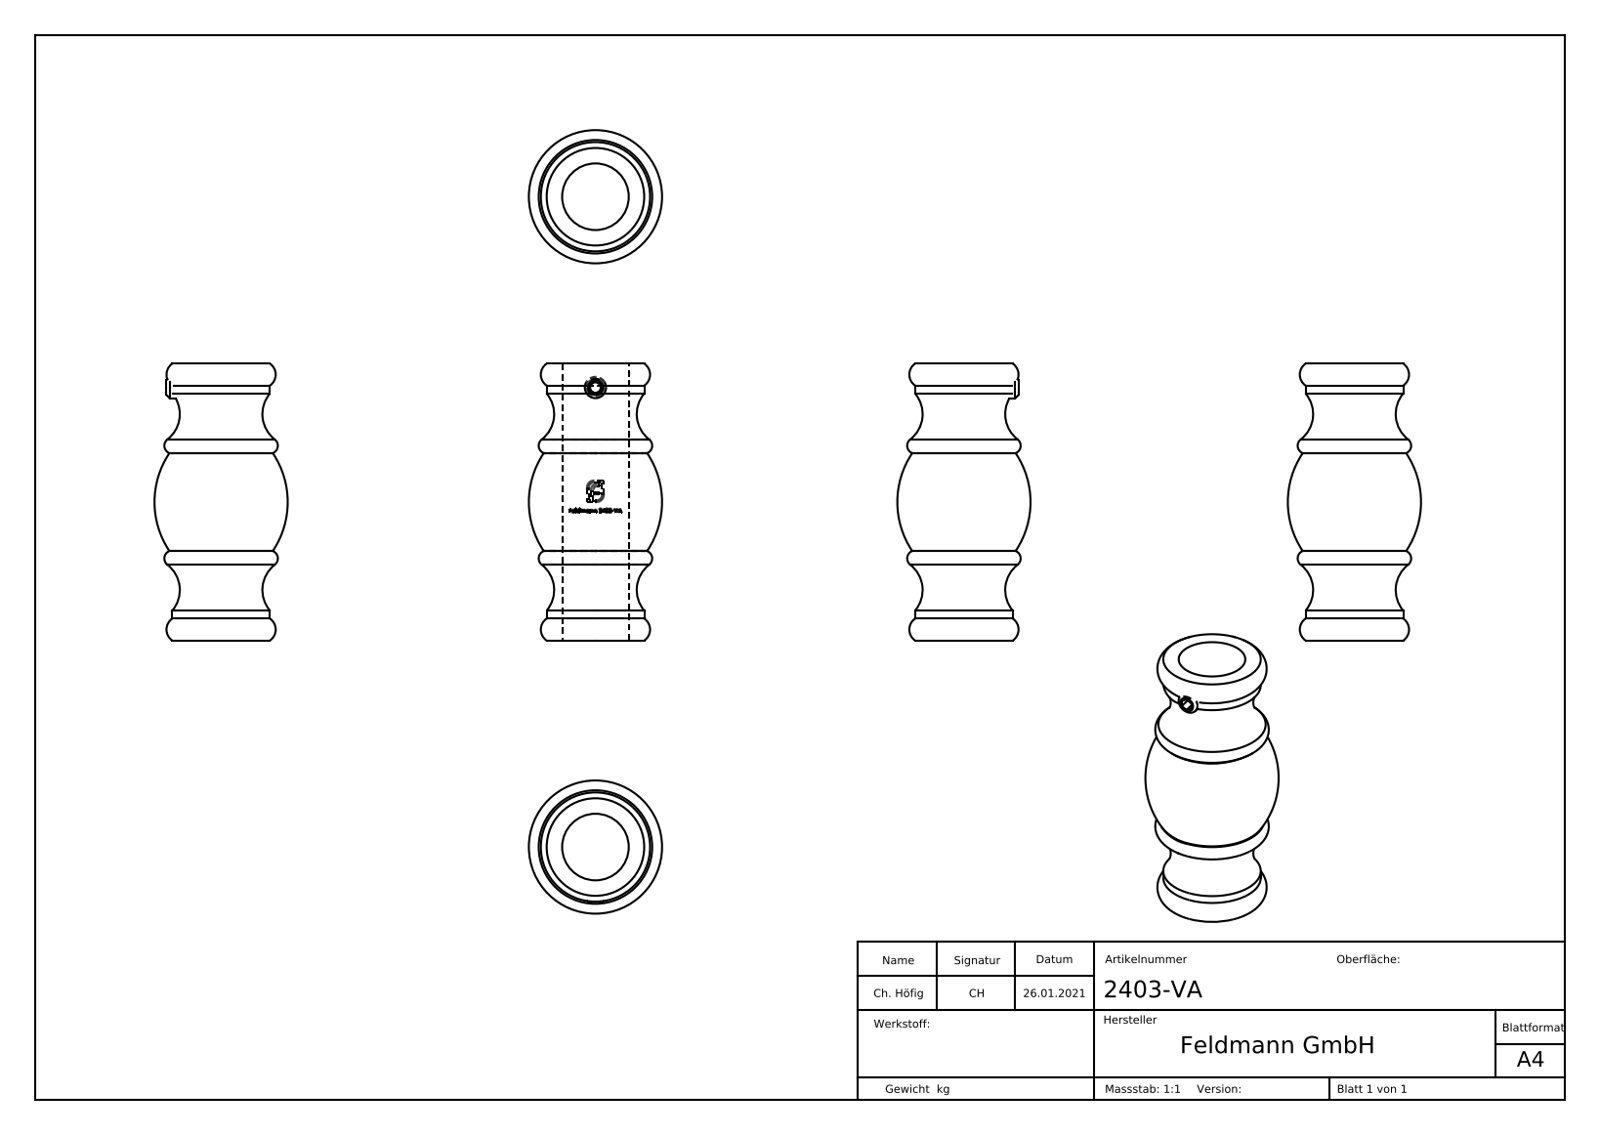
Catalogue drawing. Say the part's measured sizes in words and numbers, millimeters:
The part is named "2403-VA; DIN913_DIN 913 M4x4; 2403-VA Teil1_2403-VA Teil1; DIN913 (+1 more)". Its 3-D file was written by "SolidWorks 2018 (CONFIG_CONTROL_DESIGN)". It is 2 solids with 297 faces: 134 planar, 34 cylindrical and 129 other. Overall it measures 70.25 by 52 by 25 millimeters. Its volume is 10 321 cubic millimeters and its surface area 6 044 square millimeters. Round holes: 1 of diameter 3.3, 1 of diameter 12.5. Round bosses or shafts: 1 of diameter 18.3, 1 of diameter 4. Partial cylindrical surfaces (rounded edges, fillets, slot ends): 1 of radius 6.35. The main face-to-face distances are 52, 2, 4, 0.32, 2.84, 2.59, 2.27, 0.57, 1.89, 1.5.
